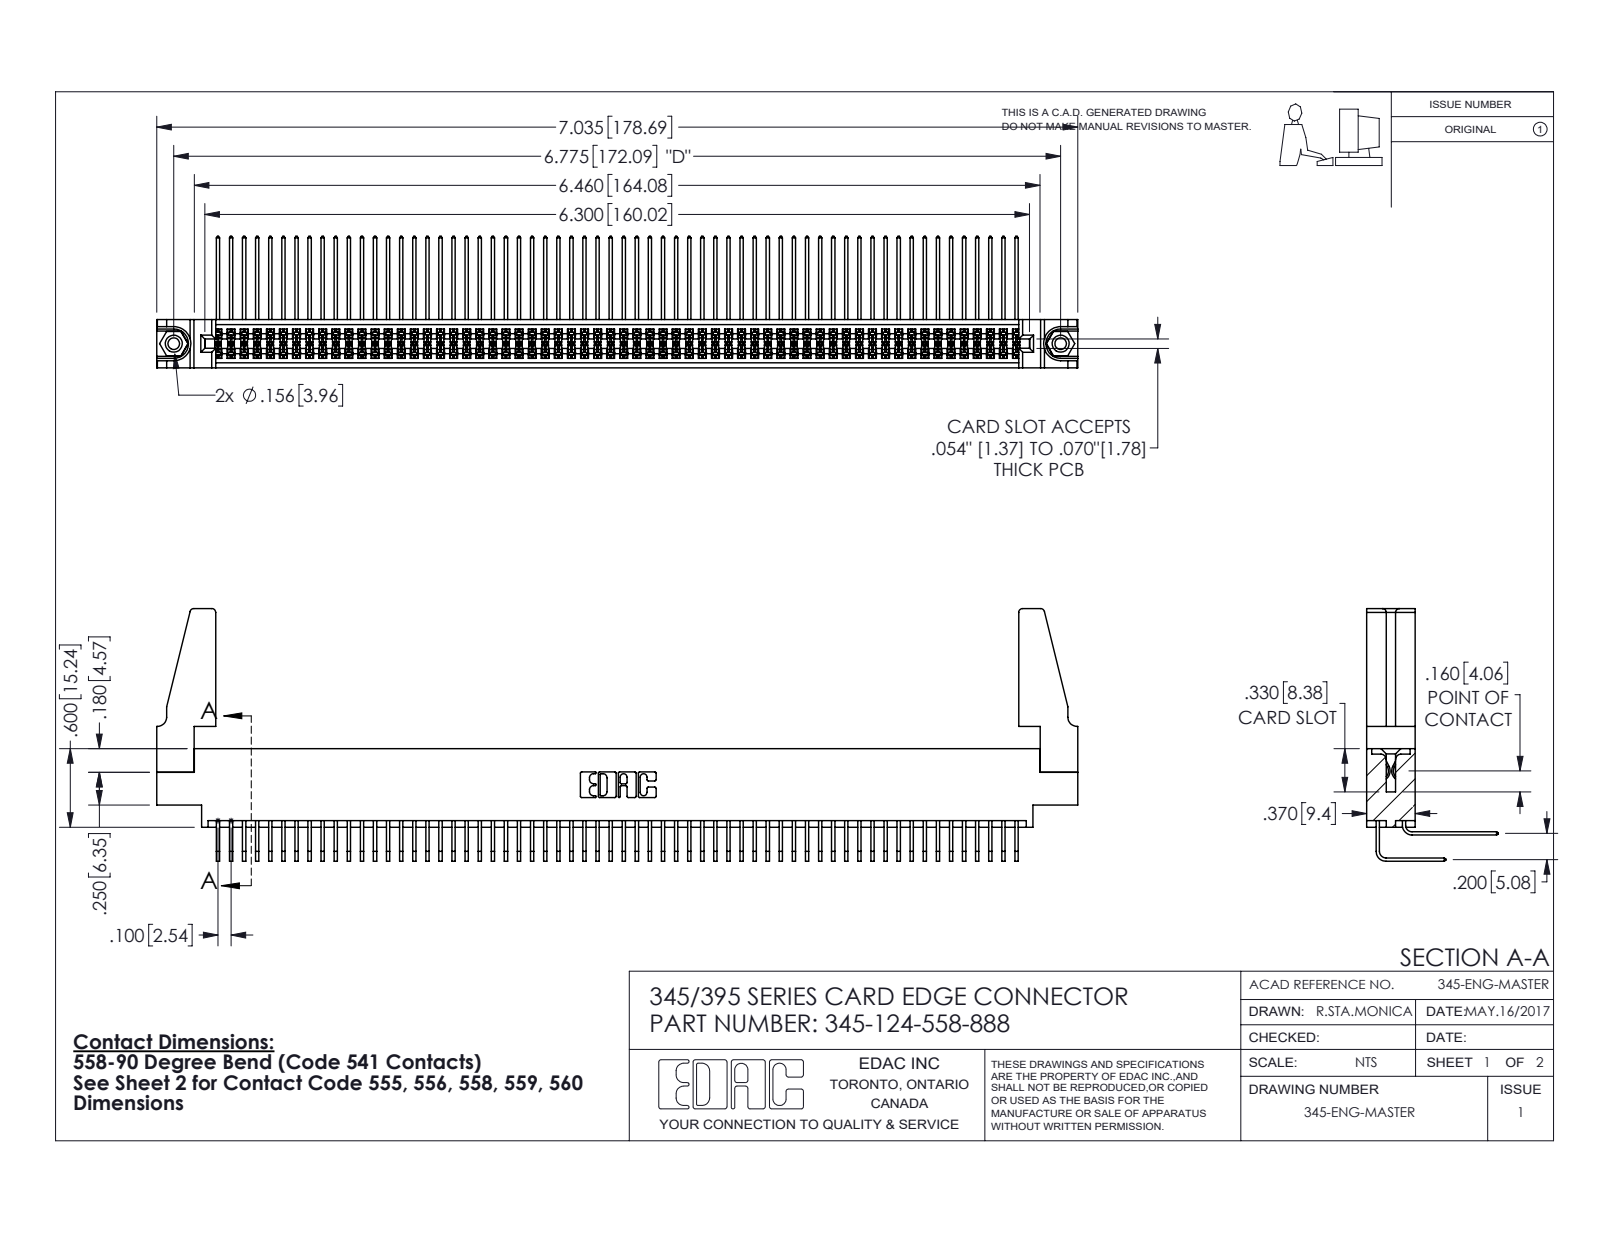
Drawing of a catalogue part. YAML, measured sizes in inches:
part_name: "345-292-001_558 Tail - 2; 345 Part_0.170 Offset - 0.156 Dia-TH; 345-250-001_345-250-001-102; 345-124-558-888 (+2 more)"
step_written_by: "SolidWorks 2016 (CONFIG_CONTROL_DESIGN)"
units: inches
bodies: {solids: 129, faces: 6702, planar: 4496, cylindrical: 2190, other: 16}
overall_size: [7.036, 1.929, 1.005]
volume: 1.306
surface_area: 52.46
round_holes:
  - {diameter: 0.089, count: 2}
  - {diameter: 0.125, count: 2}
  - {diameter: 0.156, count: 2}
  - {diameter: 0.064, count: 1}
round_bosses_or_shafts:
  - {diameter: 0.155, count: 2}
partial_cylinders:
  - {radius: 0.006, count: 248}
  - {radius: 0.01, count: 22}
  - {radius: 0.03, count: 8}
  - {radius: 0.007, count: 6}
  - {radius: 0.031, count: 6}
  - {radius: 0.026, count: 3}
  - {radius: 0.014, count: 2}
  - {radius: 0.019, count: 2}
face_to_face_distances: [0.072, 0.298, 0.2, 0.37, 0.098, 0.272, 0.025, 0.225, 0.175, 0.025]
hole_center_spacings: [0.27, 6.539, 6.775]
